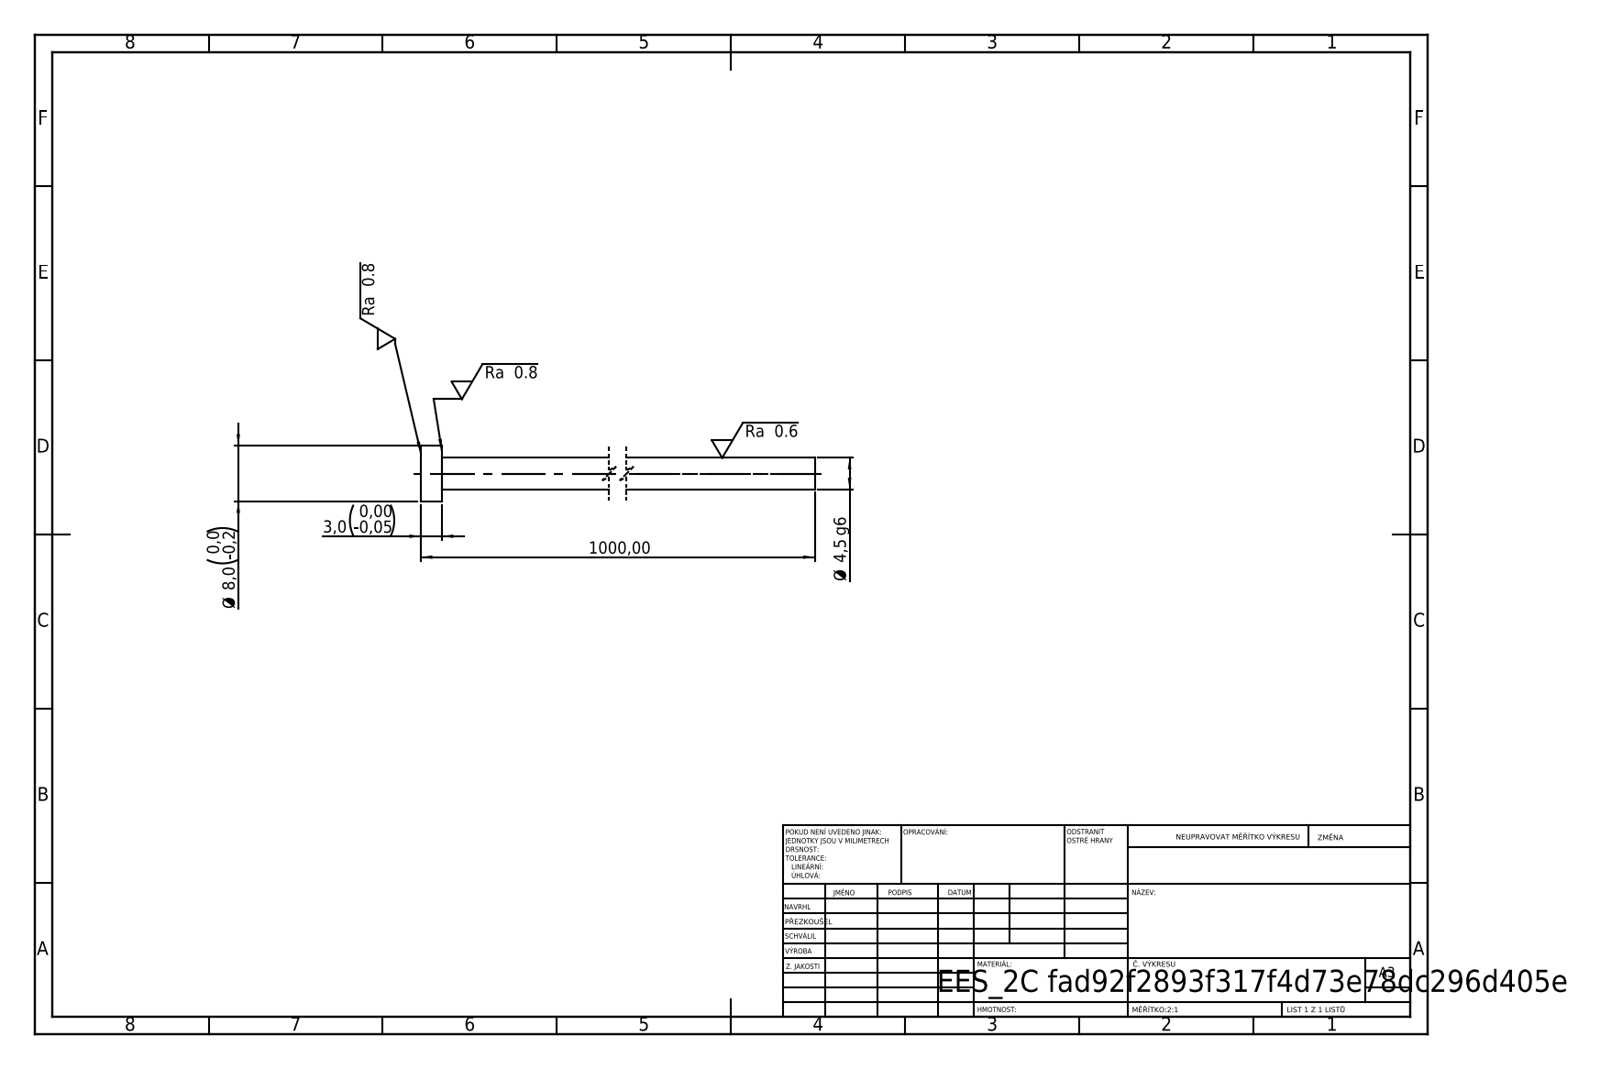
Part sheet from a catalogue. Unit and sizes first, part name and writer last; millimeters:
Units: millimetres
Overall size (bounding box): 1000 × 8 × 8
Round bosses / shafts (diameter × count): ⌀8 ×1, ⌀4.5 ×1
Main face-to-face distances: 3, 1000, 997
Volume: 16 007 mm³ · Surface area: 14 271 mm²
Bodies: 1 solid, 7 faces (3 planar, 4 cylindrical, 0 other)
STEP written by: SolidWorks 2019 (CONFIG_CONTROL_DESIGN)
